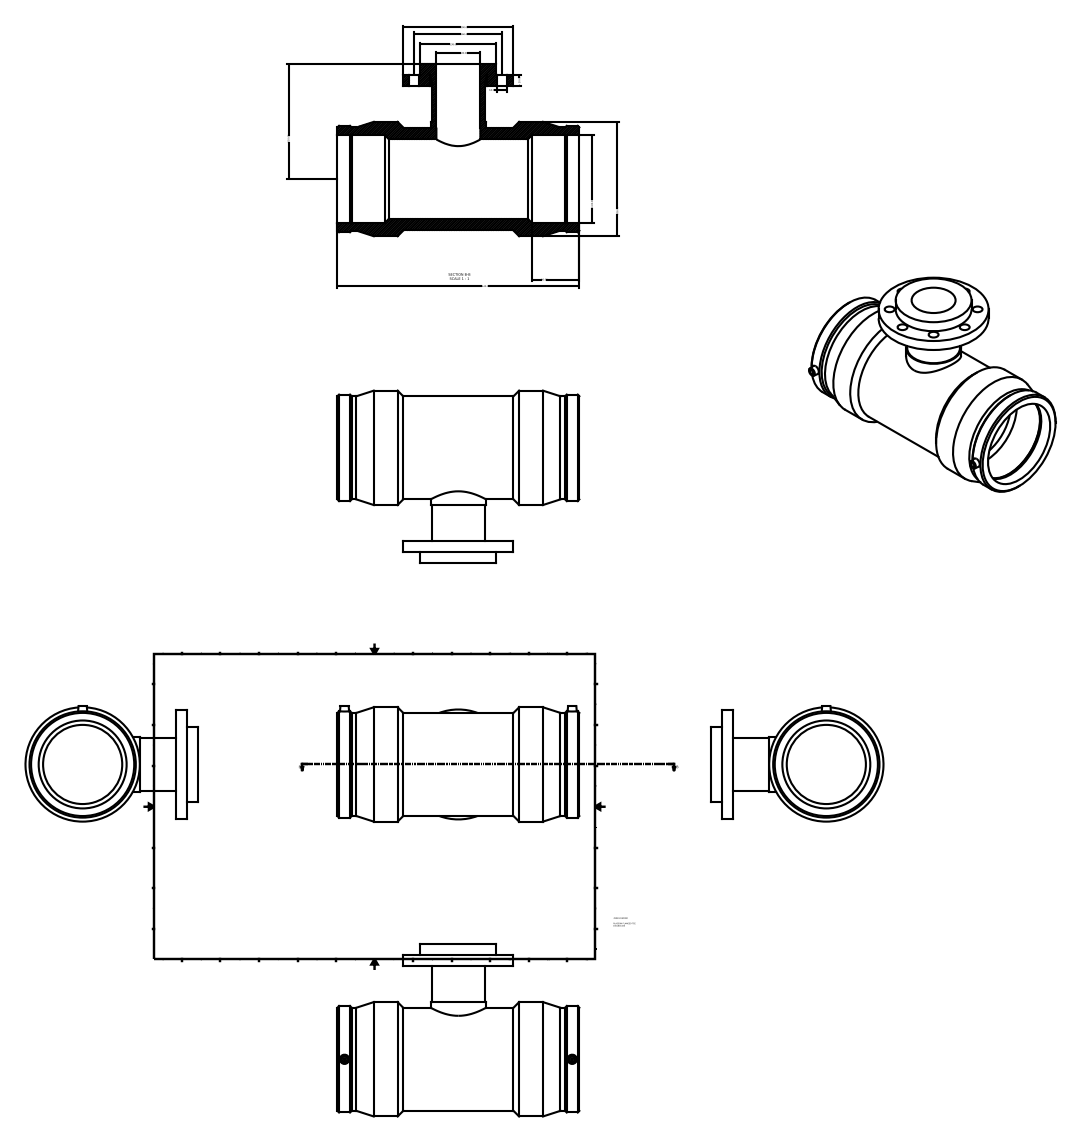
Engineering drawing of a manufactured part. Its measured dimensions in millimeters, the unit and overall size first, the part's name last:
Units: millimetres
Overall size (bounding box): 440 × 314 × 210
Round holes (diameter × count): ⌀18 ×8, ⌀10 ×2, ⌀80 ×1, ⌀104 ×1, ⌀144 ×1, ⌀160 ×1
Round bosses / shafts (diameter × count): ⌀4 ×2, ⌀208 ×1, ⌀200 ×1, ⌀193.44 ×1, ⌀187.64 ×1, ⌀187.2 ×1, ⌀138 ×1, ⌀100 ×1
Main face-to-face distances: 20, 40, 440, 26.42, 413.58, 106, 86, 66, 387.16, 14
Hole centre spacings: 61.23, 80, 113.14, 147.82, 160, 414.2
Volume: 5 928 000 mm³ · Surface area: 644 825 mm²
Bodies: 1 solid, 60 faces (14 planar, 30 cylindrical, 16 other)
Part name (STEP PRODUCT): 499404160080
STEP written by: Autodesk Inventor 2015 (AUTOMOTIVE_DESIGN)
